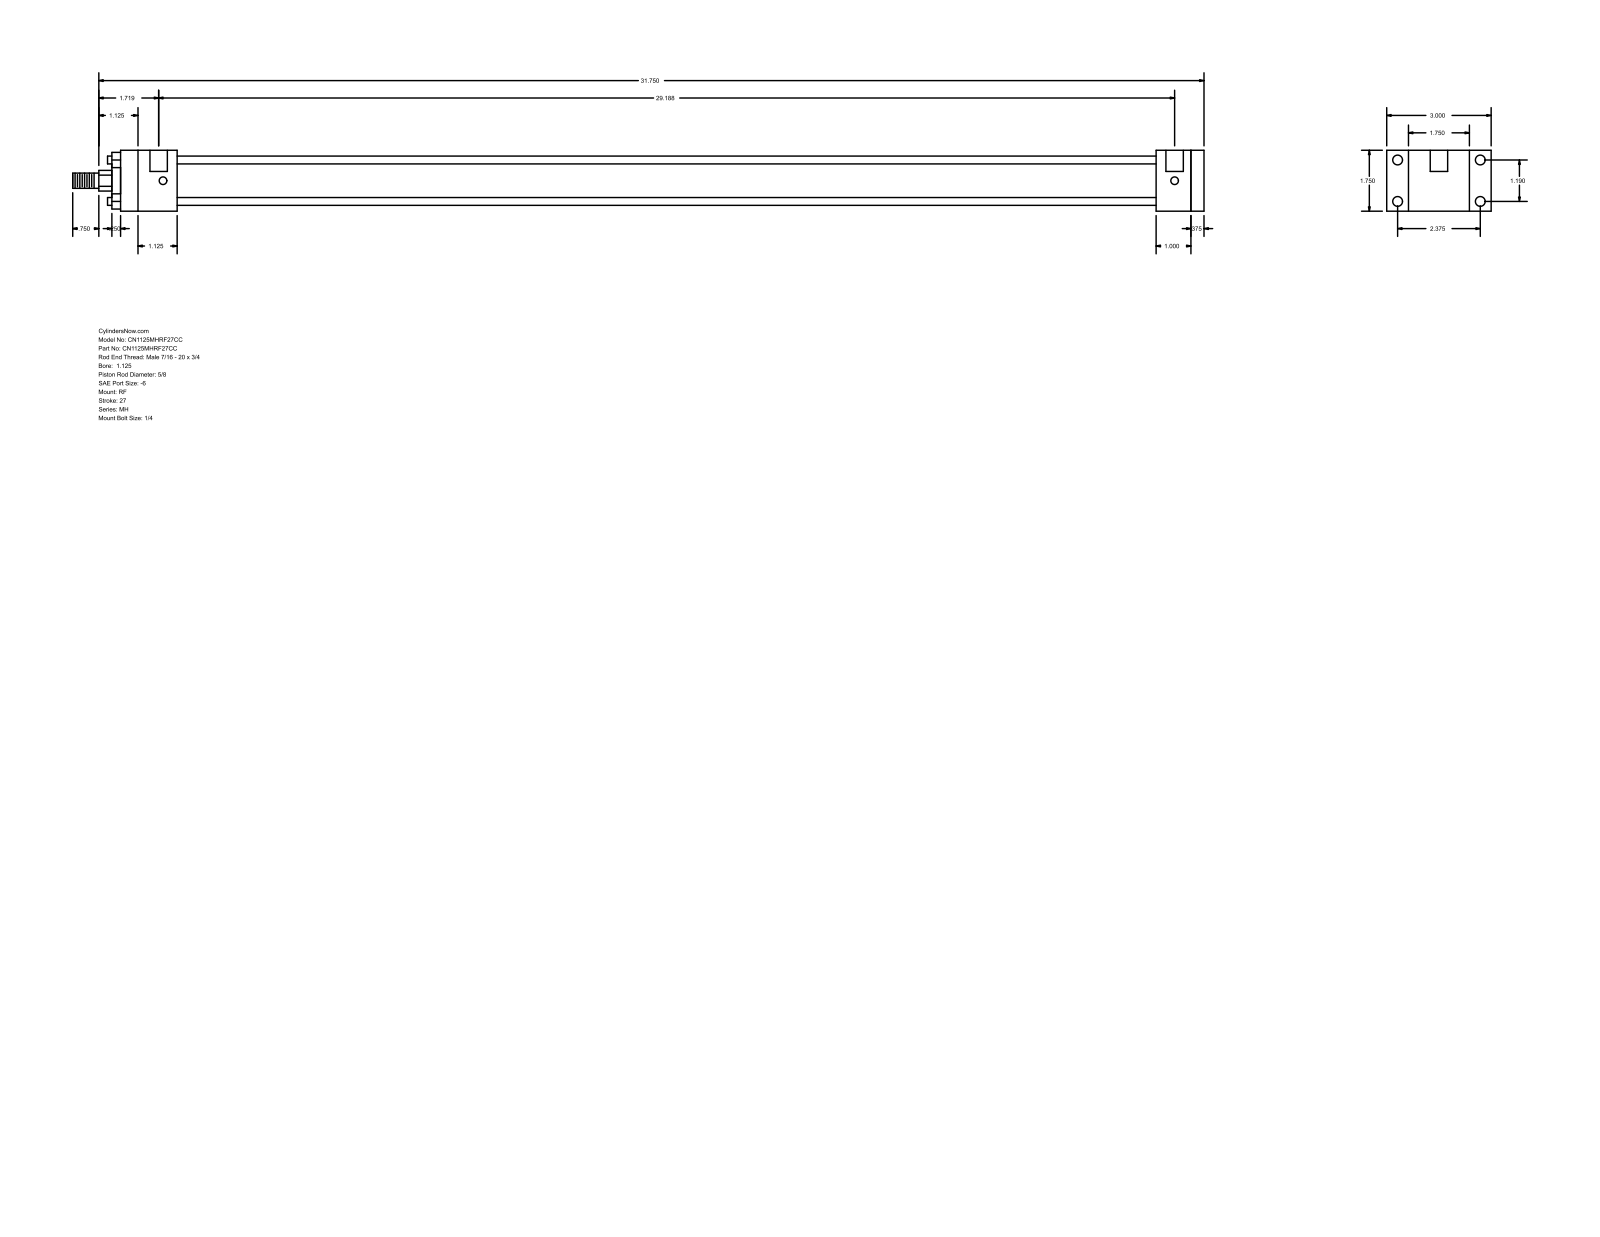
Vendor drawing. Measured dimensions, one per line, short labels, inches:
name: MH_RF__0112_0.625
written by: GSSL Pune (CONFIG_CONTROL_DESIGN)
unit: in
bodies: 0 solids, 92 faces (64 planar, 28 cylindrical, 0 other)
size: 32.5 × 3 × 1.75
holes: 4× ⌀0.219, 4× ⌀0.281, 2× ⌀0.5
bosses: 4× ⌀0.225, 1× ⌀1.375, 1× ⌀1.125, 1× ⌀0.625, 1× ⌀0.437
rounds: 1× R0.297
face distances: 1.75, 0.375, 31.125, 1, 1.375, 0.625, 29.125, 29.5, 28.125, 1.625
hole spacings: 1.19, 2.375, 2.656, 29.063, 0.125, 29.187
